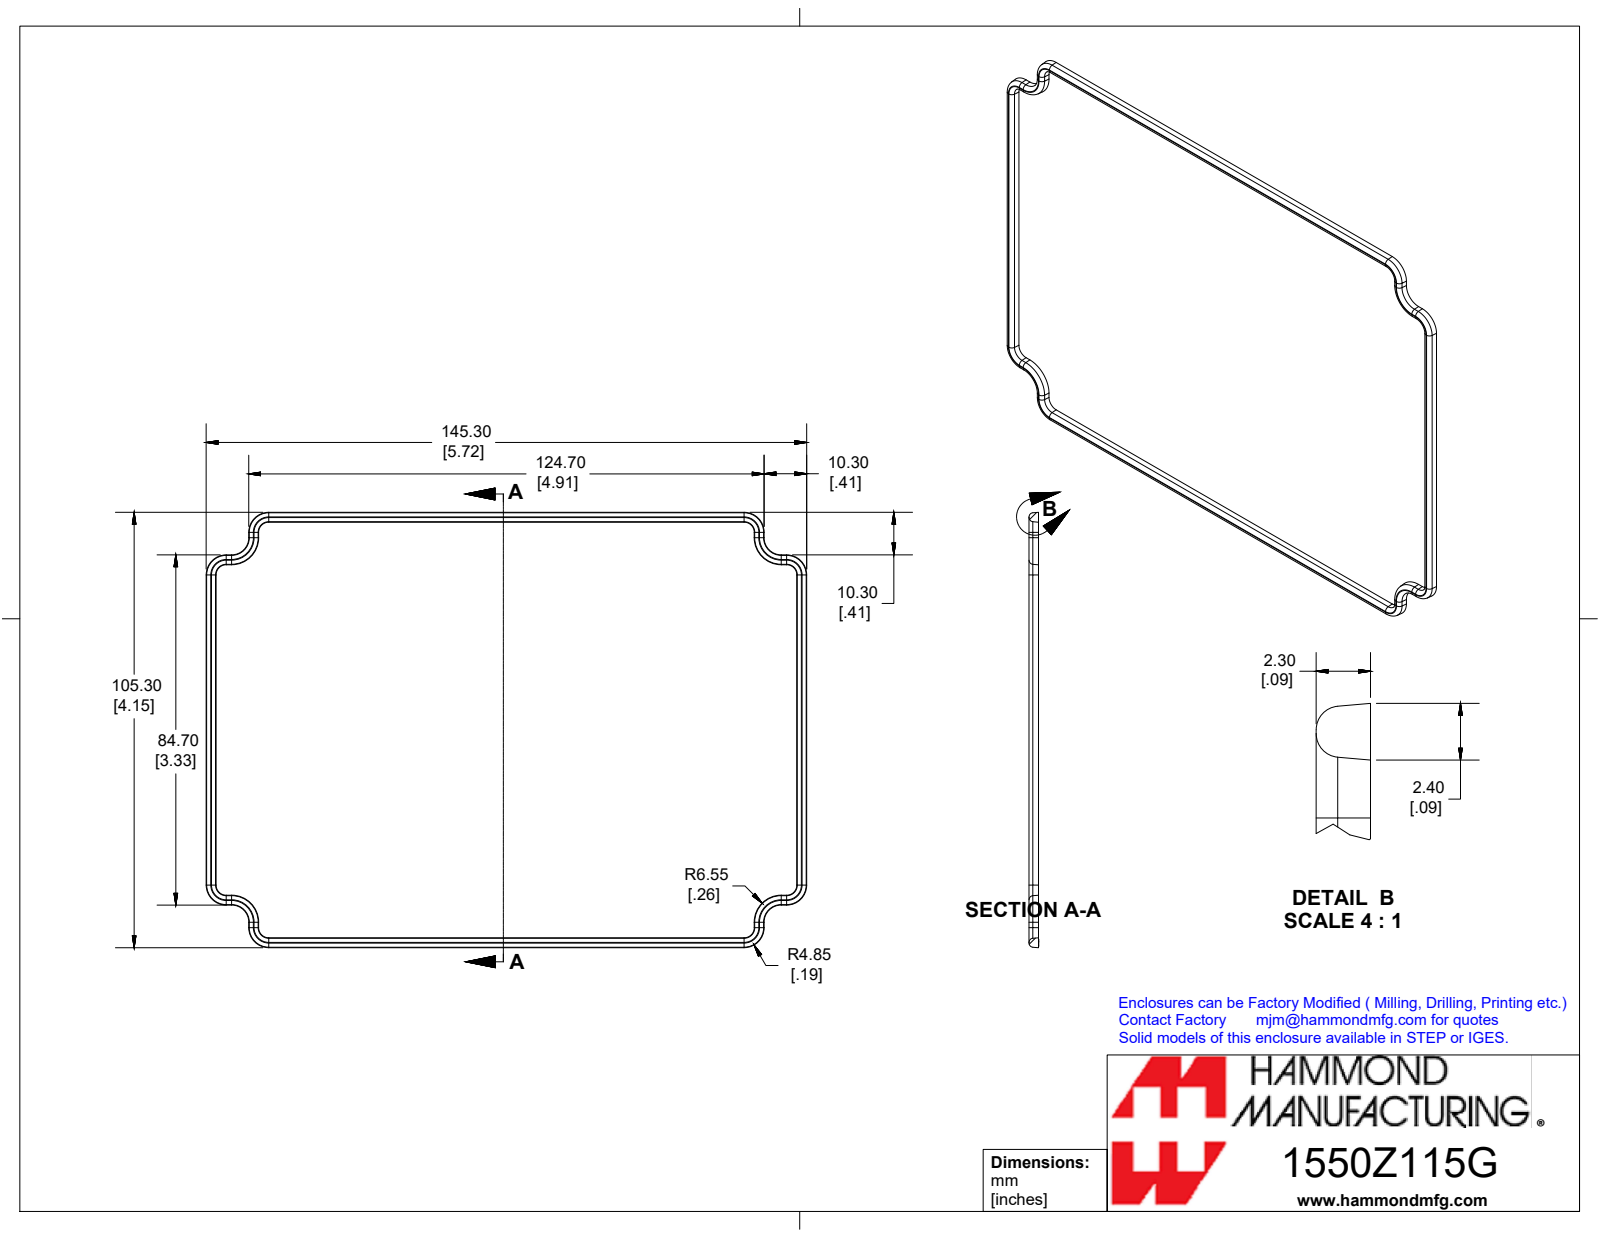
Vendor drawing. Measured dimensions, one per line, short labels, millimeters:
name: 1550Z115GASKET
written by: SolidWorks 2019 (CONFIG_CONTROL_DESIGN)
unit: mm
bodies: 1 solid, 153 faces (44 planar, 24 cylindrical, 85 other)
size: 145.3 × 105.3 × 2.4
volume: 2 210 mm³; area: 3 909 mm²
rounds: 16× R1
face distances: 102.5, 142.3, 2.3, 10.3, 92.2, 132.1, 82, 121.8, 2.4, 1.7
